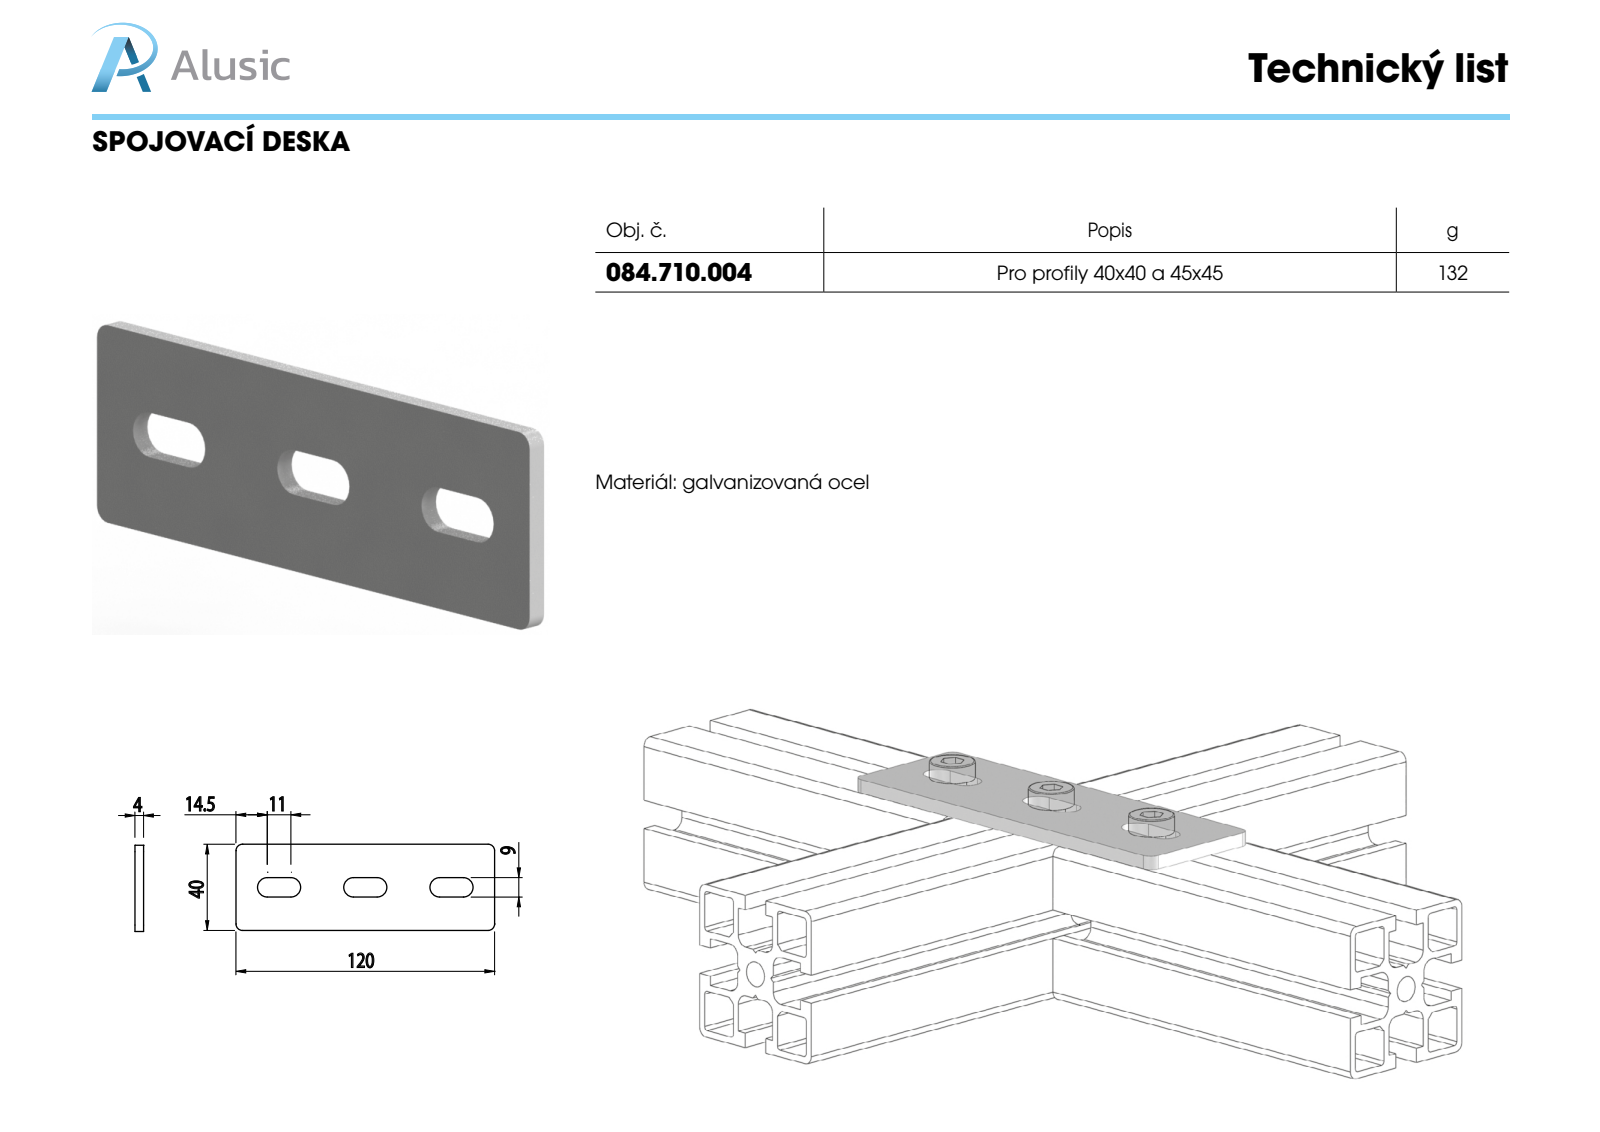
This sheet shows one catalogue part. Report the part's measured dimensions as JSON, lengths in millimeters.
{"part_name": "084.710.004", "step_written_by": "SolidWorks 2011 (CONFIG_CONTROL_DESIGN)", "units": "millimeters", "bodies": {"solids": 1, "faces": 22, "planar": 12, "cylindrical": 10, "other": 0}, "overall_size": [120, 40, 4], "volume_mm3": 17218, "surface_area_mm2": 10472, "partial_cylinders_radius": [[4.5, 6], [3, 4]], "face_to_face_distances": [4, 40, 15.5, 24.5, 120, 9]}
